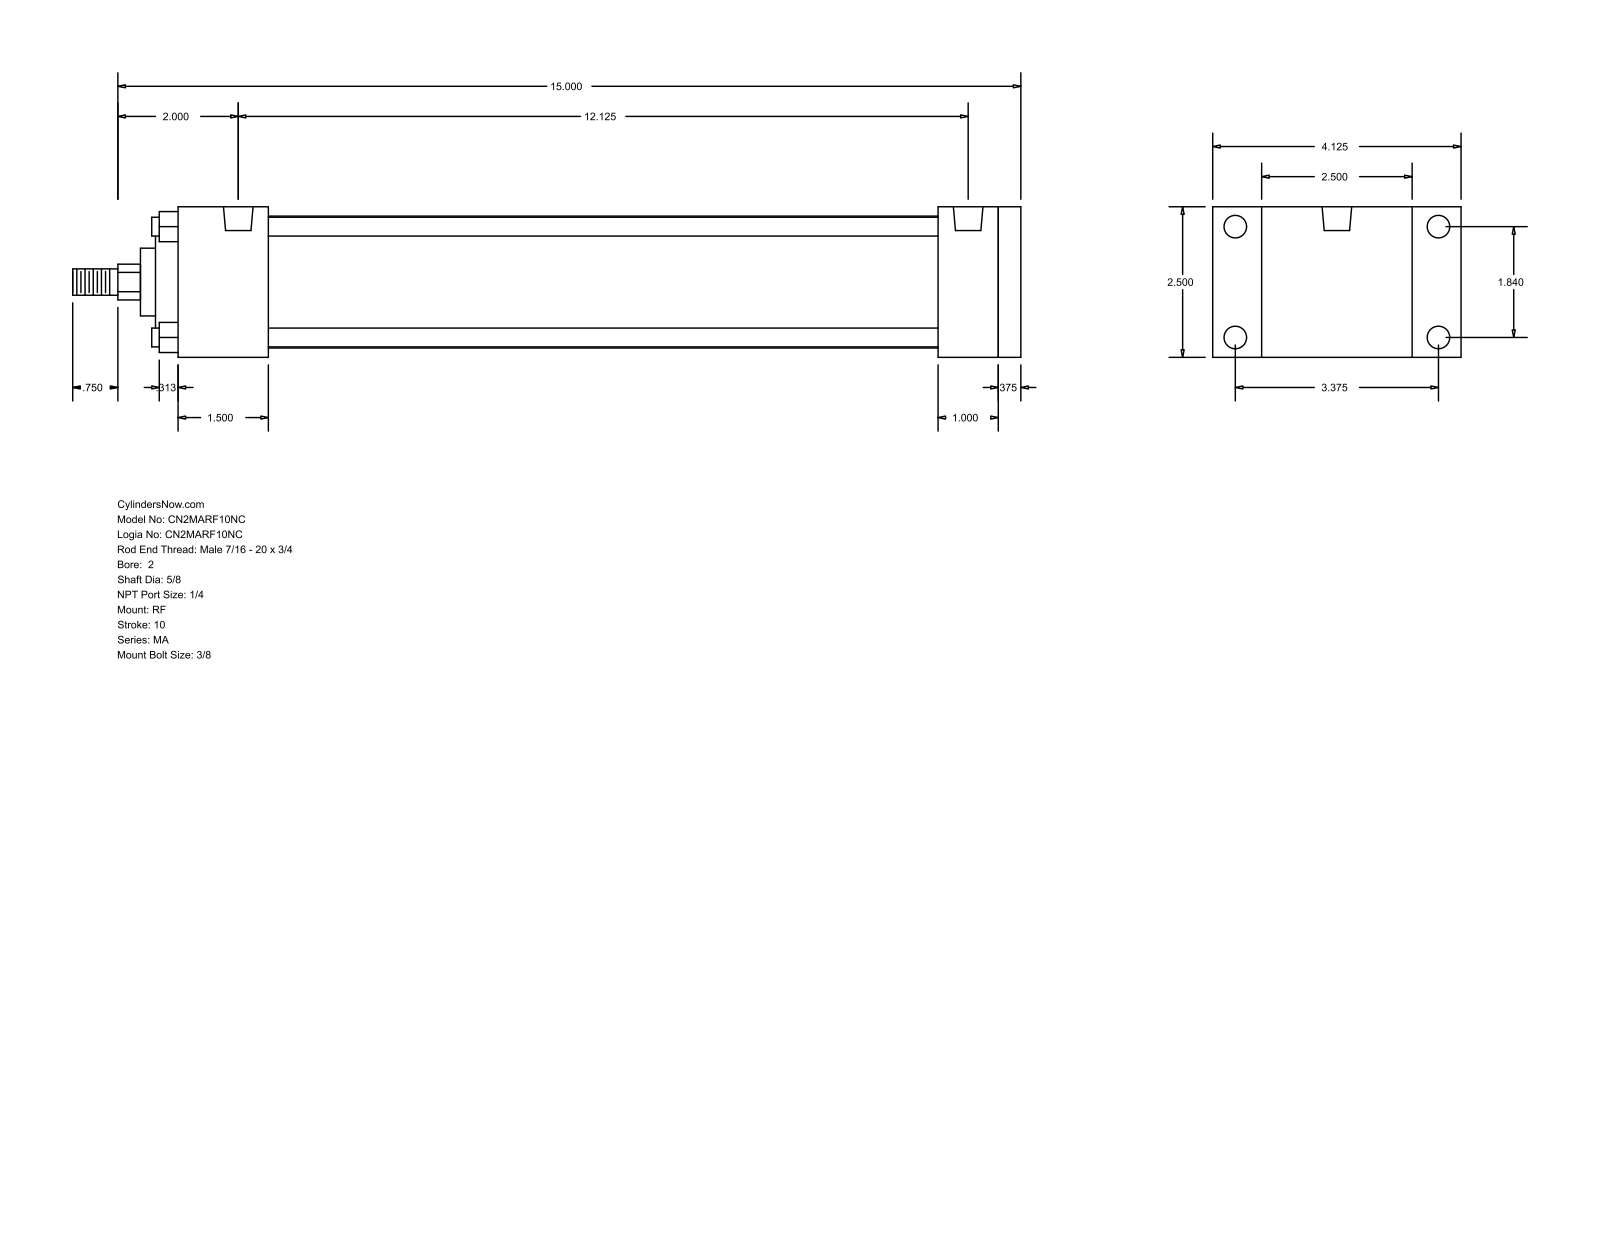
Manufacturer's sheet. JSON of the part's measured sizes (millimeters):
{"part_name": "MA_RF__0200_0.625", "step_written_by": "GSSL Pune (CONFIG_CONTROL_DESIGN)", "units": "millimeters", "bodies": {"solids": 0, "faces": 94, "planar": 65, "cylindrical": 29, "other": 0}, "overall_size": [400.05, 104.78, 63.5], "round_holes": [[7.94, 4], [9.53, 4], [12.49, 2]], "round_bosses_or_shafts": [[7.94, 4], [55.63, 1], [50.8, 1], [28.57, 1], [15.88, 1], [11.11, 1]], "partial_cylinders_radius": [[7.54, 1]], "face_to_face_distances": [63.5, 9.52, 355.6, 38.1, 34.93, 365.12, 346.08, 307.98, 317.5, 320.67], "hole_center_spacings": [46.74, 85.72, 97.63, 307.97]}
